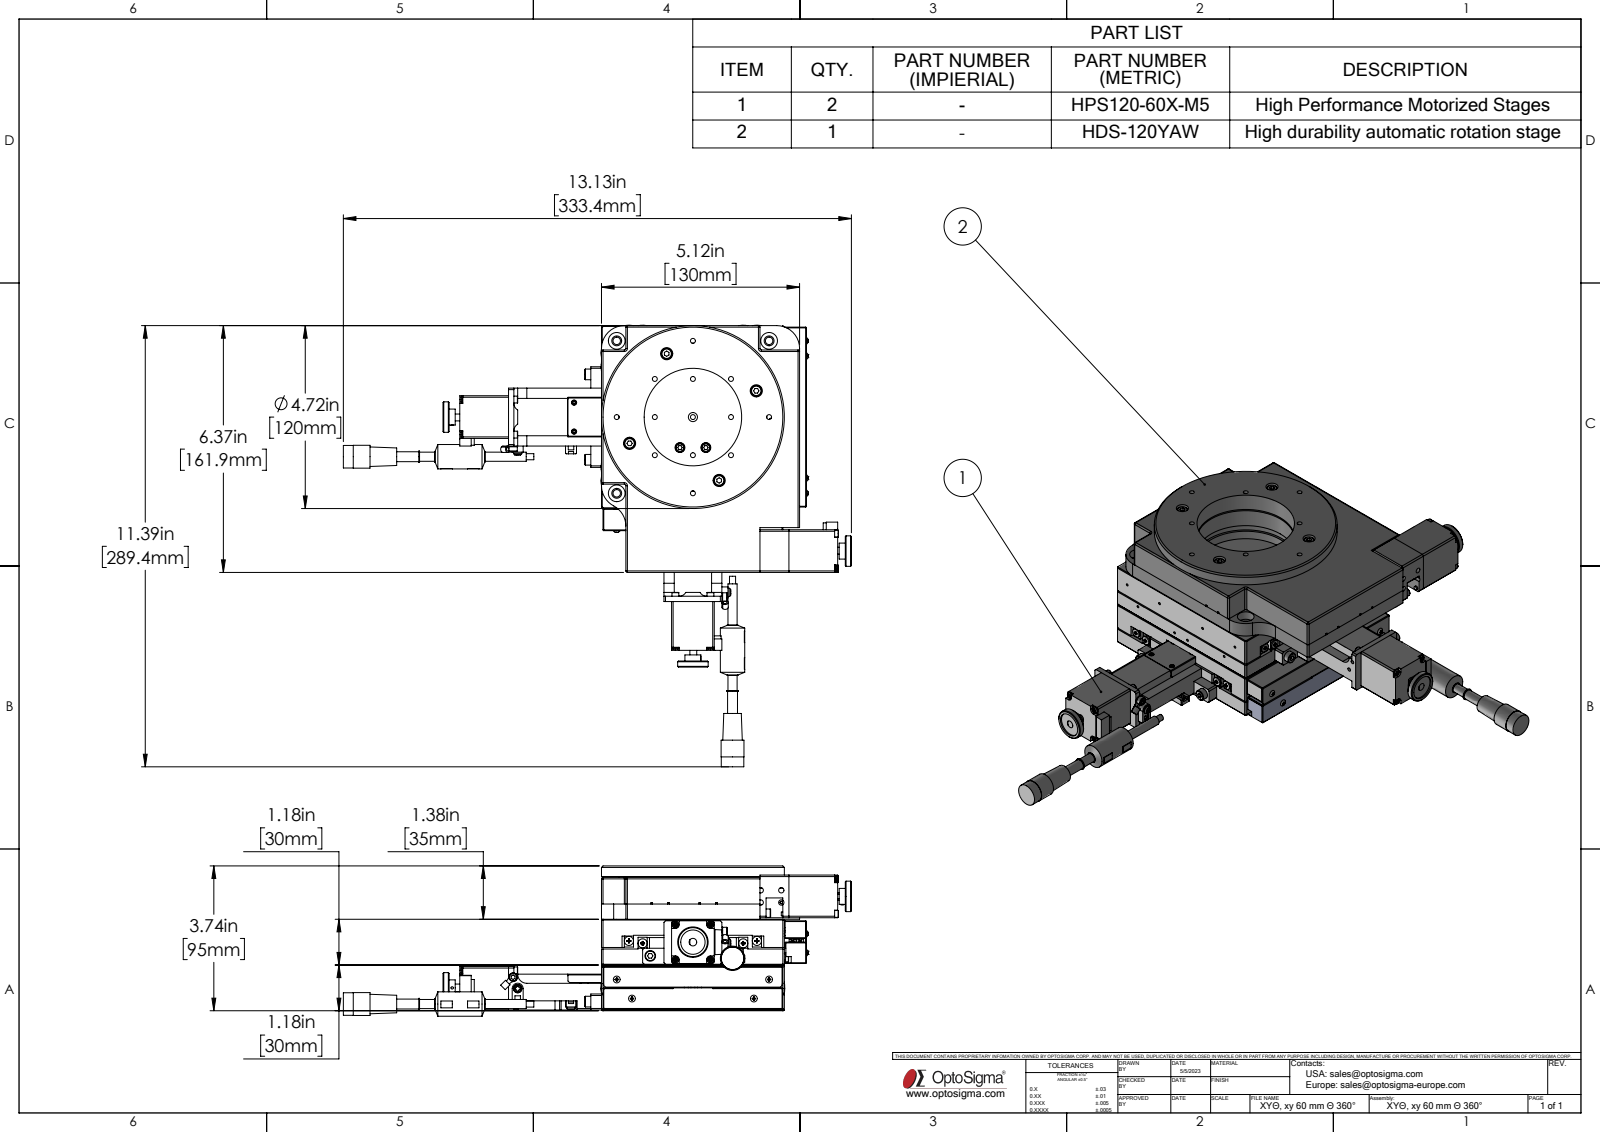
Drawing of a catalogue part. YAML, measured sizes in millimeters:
part_name: "HPS120CE-M02-14001-S12^HPS120-60X-M5_STP(2)_HPS120-60X-M5; XY, xy 60 mm 360; HPS120-60X-M5_STP(2)^HPS120-60X-M5; HPS120-60X-M5 (+5 more)"
step_written_by: "SolidWorks 2022 (AUTOMOTIVE_DESIGN)"
units: millimeters
bodies: {solids: 32, faces: 6719, planar: 3308, cylindrical: 2109, other: 1302}
overall_size: [333.4, 289.59, 98.6]
volume: 670082
surface_area: 460771
round_holes:
  - {diameter: 2.5, count: 46}
  - {diameter: 6, count: 46}
  - {diameter: 3.3, count: 40}
  - {diameter: 1.57, count: 34}
  - {diameter: 3, count: 25}
  - {diameter: 3.24, count: 17}
  - {diameter: 4.2, count: 10}
  - {diameter: 2.46, count: 9}
  - {diameter: 2.11, count: 8}
  - {diameter: 6.5, count: 8}
  - {diameter: 1.2, count: 6}
  - {diameter: 1.57, count: 6}
round_bosses_or_shafts:
  - {diameter: 5.5, count: 64}
  - {diameter: 3, count: 55}
  - {diameter: 4.5, count: 21}
  - {diameter: 2, count: 15}
  - {diameter: 6, count: 14}
  - {diameter: 7, count: 10}
  - {diameter: 3.8, count: 10}
  - {diameter: 4, count: 6}
partial_cylinders:
  - {radius: 0.5, count: 121}
  - {radius: 0.3, count: 64}
  - {radius: 1, count: 33}
  - {radius: 0.7, count: 32}
  - {radius: 3, count: 26}
  - {radius: 5, count: 17}
  - {radius: 1.4, count: 16}
  - {radius: 0.8, count: 12}
face_to_face_distances: [30, 10.5, 19.5, 6.5, 7.5, 25, 18, 0.8, 0.5, 11.5]
hole_center_spacings: [8.5, 10, 1.5, 9.34, 16.04, 18.5, 27.02, 46]
